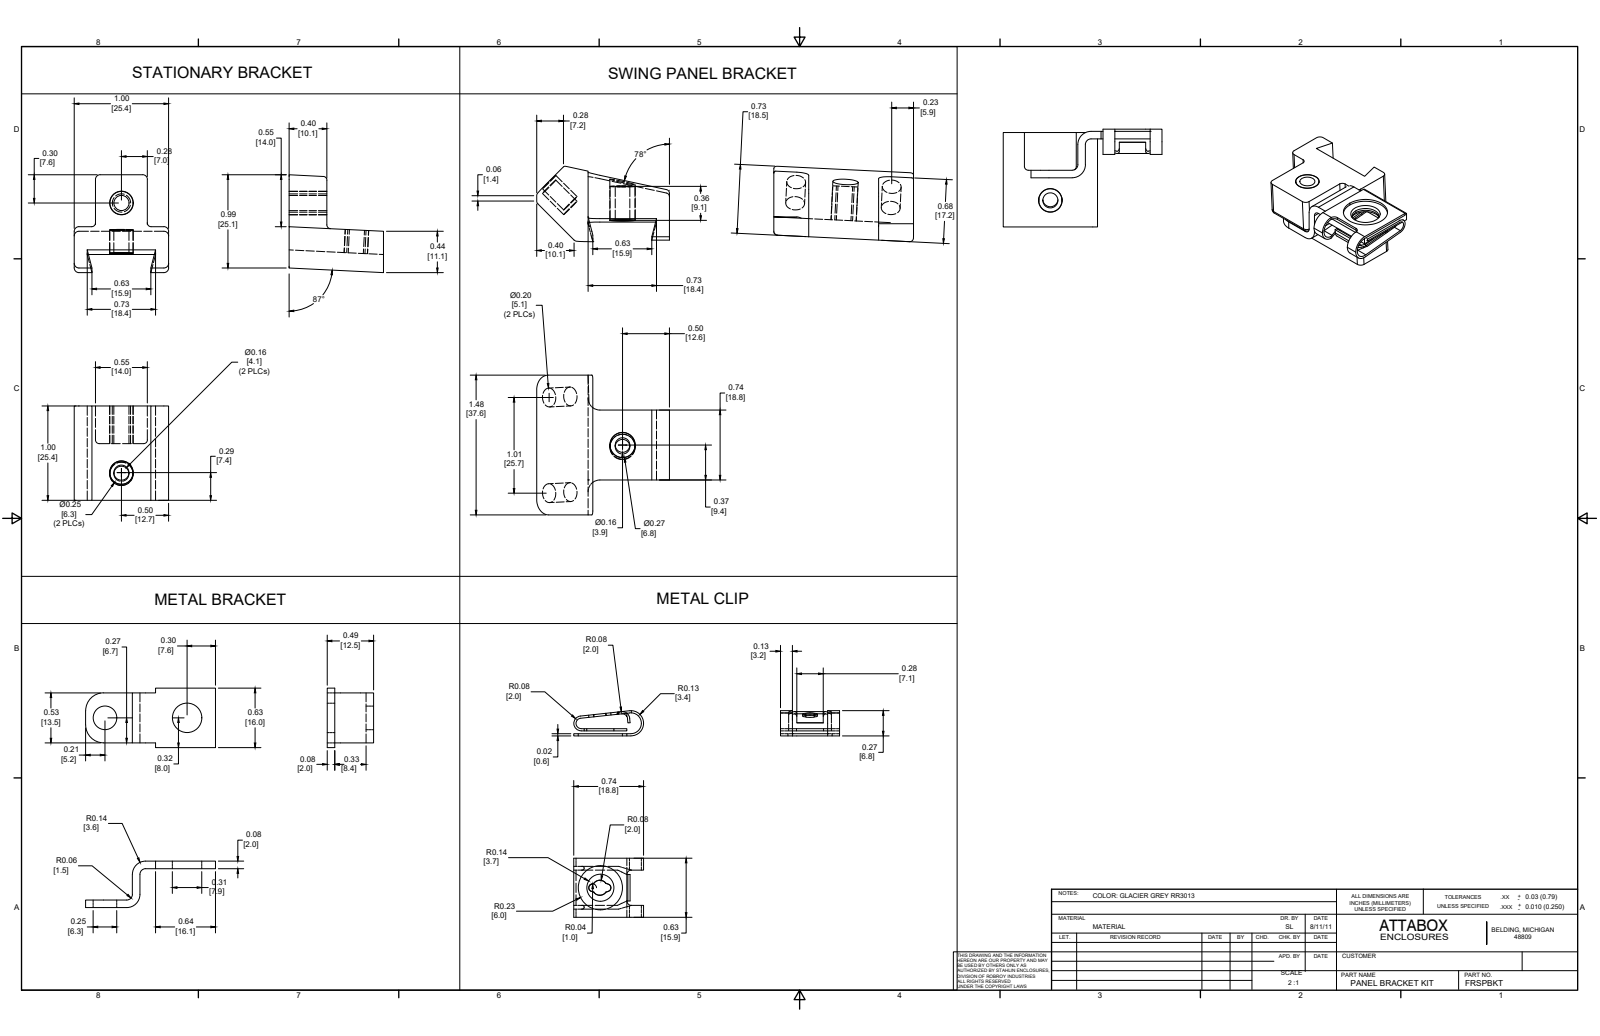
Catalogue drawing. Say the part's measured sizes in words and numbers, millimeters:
The part is named "FRSPBKT". Its 3-D file was written by "SolidWorks 2019 (AUTOMOTIVE_DESIGN)". It is 16 solids with 416 faces: 164 planar, 154 cylindrical and 98 other. Overall it measures 209.9 by 203.5 by 44 millimeters. Its volume is 41 670 cubic millimeters and its surface area 24 630 square millimeters. Round holes: 6 of diameter 6.4, 2 of diameter 4, 2 of diameter 6.4, 2 of diameter 7.9, 2 of diameter 8.9. Round bosses or shafts: 6 of diameter 4.8, 4 of diameter 8, 2 of diameter 9.5, 2 of diameter 6.2. Partial cylindrical surfaces (rounded edges, fillets, slot ends): 50 of radius 0.3, 28 of radius 1.5, 10 of radius 1.6, 8 of radius 0.6, 8 of radius 1.6, 8 of radius 3.3, 4 of radius 4.8, 2 of radius 0.8. The main face-to-face distances are 2, 2.5, 1.9, 0.5, 7.9, 10.4, 251, 5.8, 4.1, 4.4. The hole center spacings are 22.1, 144.6, 5.7, 128.5, 158.8.
